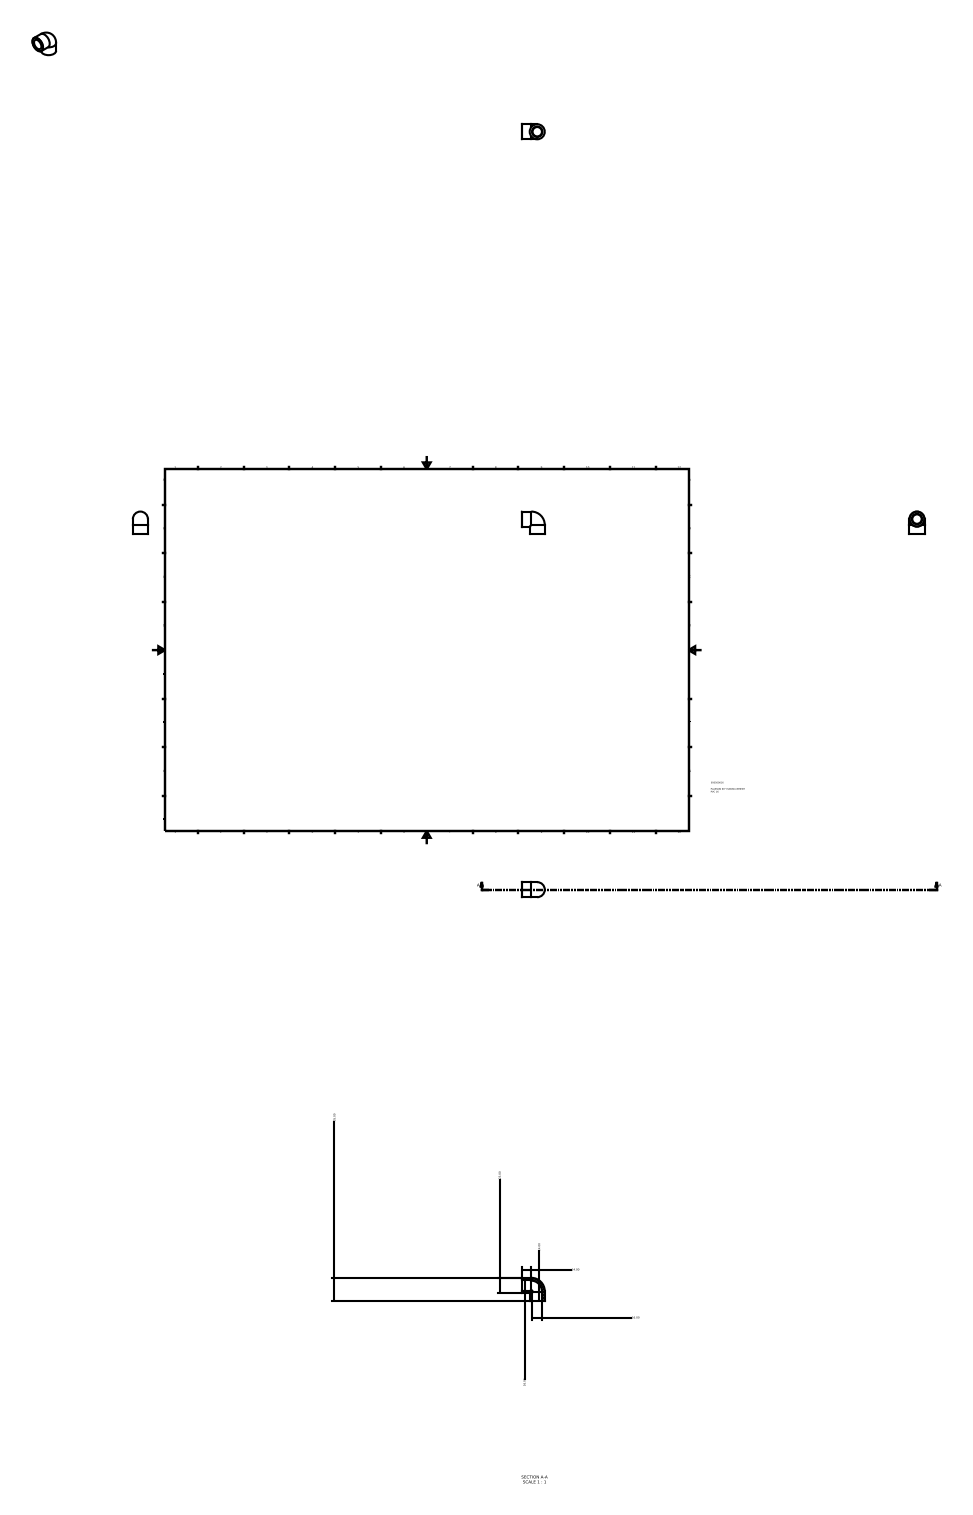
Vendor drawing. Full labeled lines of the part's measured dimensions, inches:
Part name (STEP PRODUCT): 050500016
STEP written by: Autodesk Inventor 2015 (AUTOMOTIVE_DESIGN)
Units: inches
Bodies: 1 solid, 11 faces (4 planar, 4 cylindrical, 3 other)
Overall size (bounding box): 1.378 × 1.378 × 0.906
Volume: 0.604 in³ · Surface area: 8.82 in²
Round holes (diameter × count): ⌀0.63 ×2
Round bosses / shafts (diameter × count): ⌀0.906 ×2
Main face-to-face distances: 0.551
